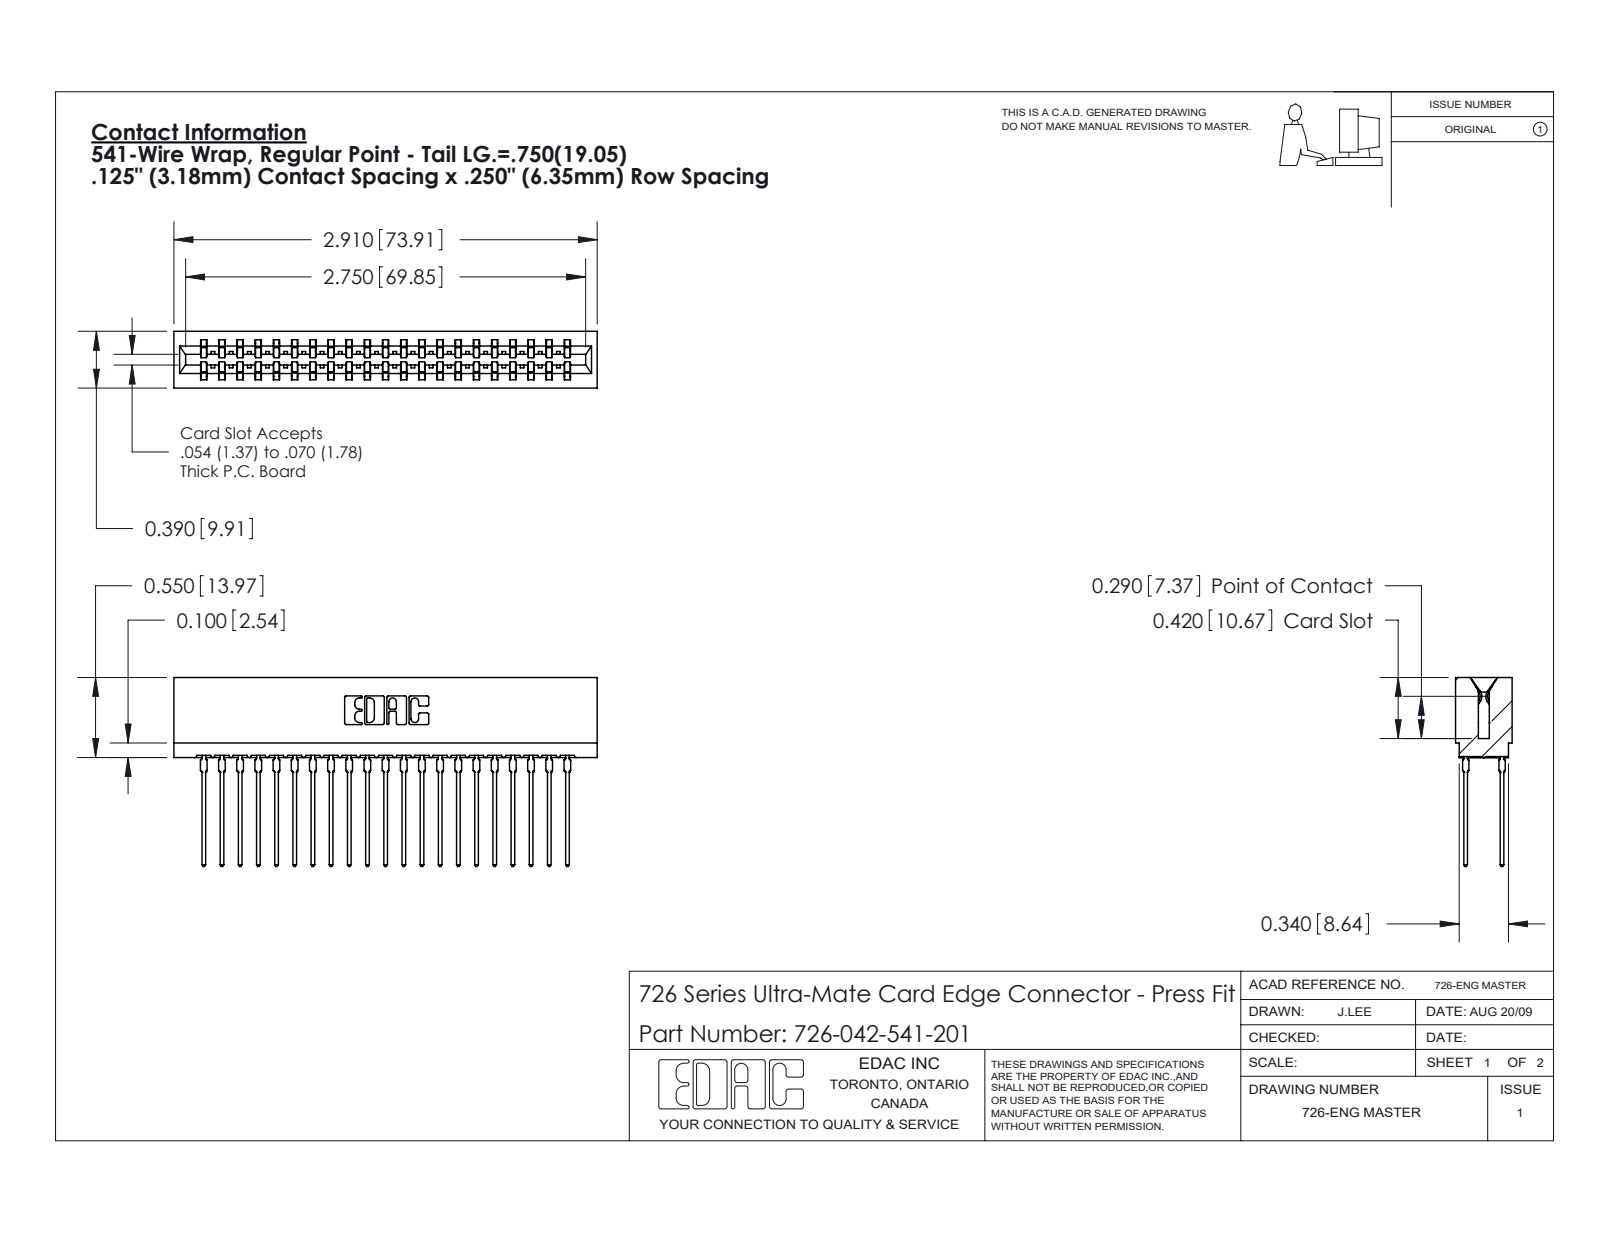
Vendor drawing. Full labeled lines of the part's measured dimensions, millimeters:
Part name (STEP PRODUCT): 726-042-541-201; 746-292-001_541; 726 Part_.515 Slot Depth - 01
STEP written by: SolidWorks 2020 (CONFIG_CONTROL_DESIGN)
Units: millimetres
Bodies: 43 solids, 3856 faces (1987 planar, 777 cylindrical, 1092 other)
Overall size (bounding box): 73.9 × 33 × 9.9
Volume: 7 140 mm³ · Surface area: 12 610 mm²
Partial cylindrical surfaces — rounded edges, fillets, slot ends (radius × count): R0.5 ×84, R0.3 ×22, R0.4 ×22, R0.1 ×8, R0.3 ×8, R0.2 ×6, R0.8 ×6, R0.7 ×3
Main face-to-face distances: 1.4, 8.5, 6.4, 0.6, 7.8, 2.1, 9.9, 7, 12.7, 19.1
